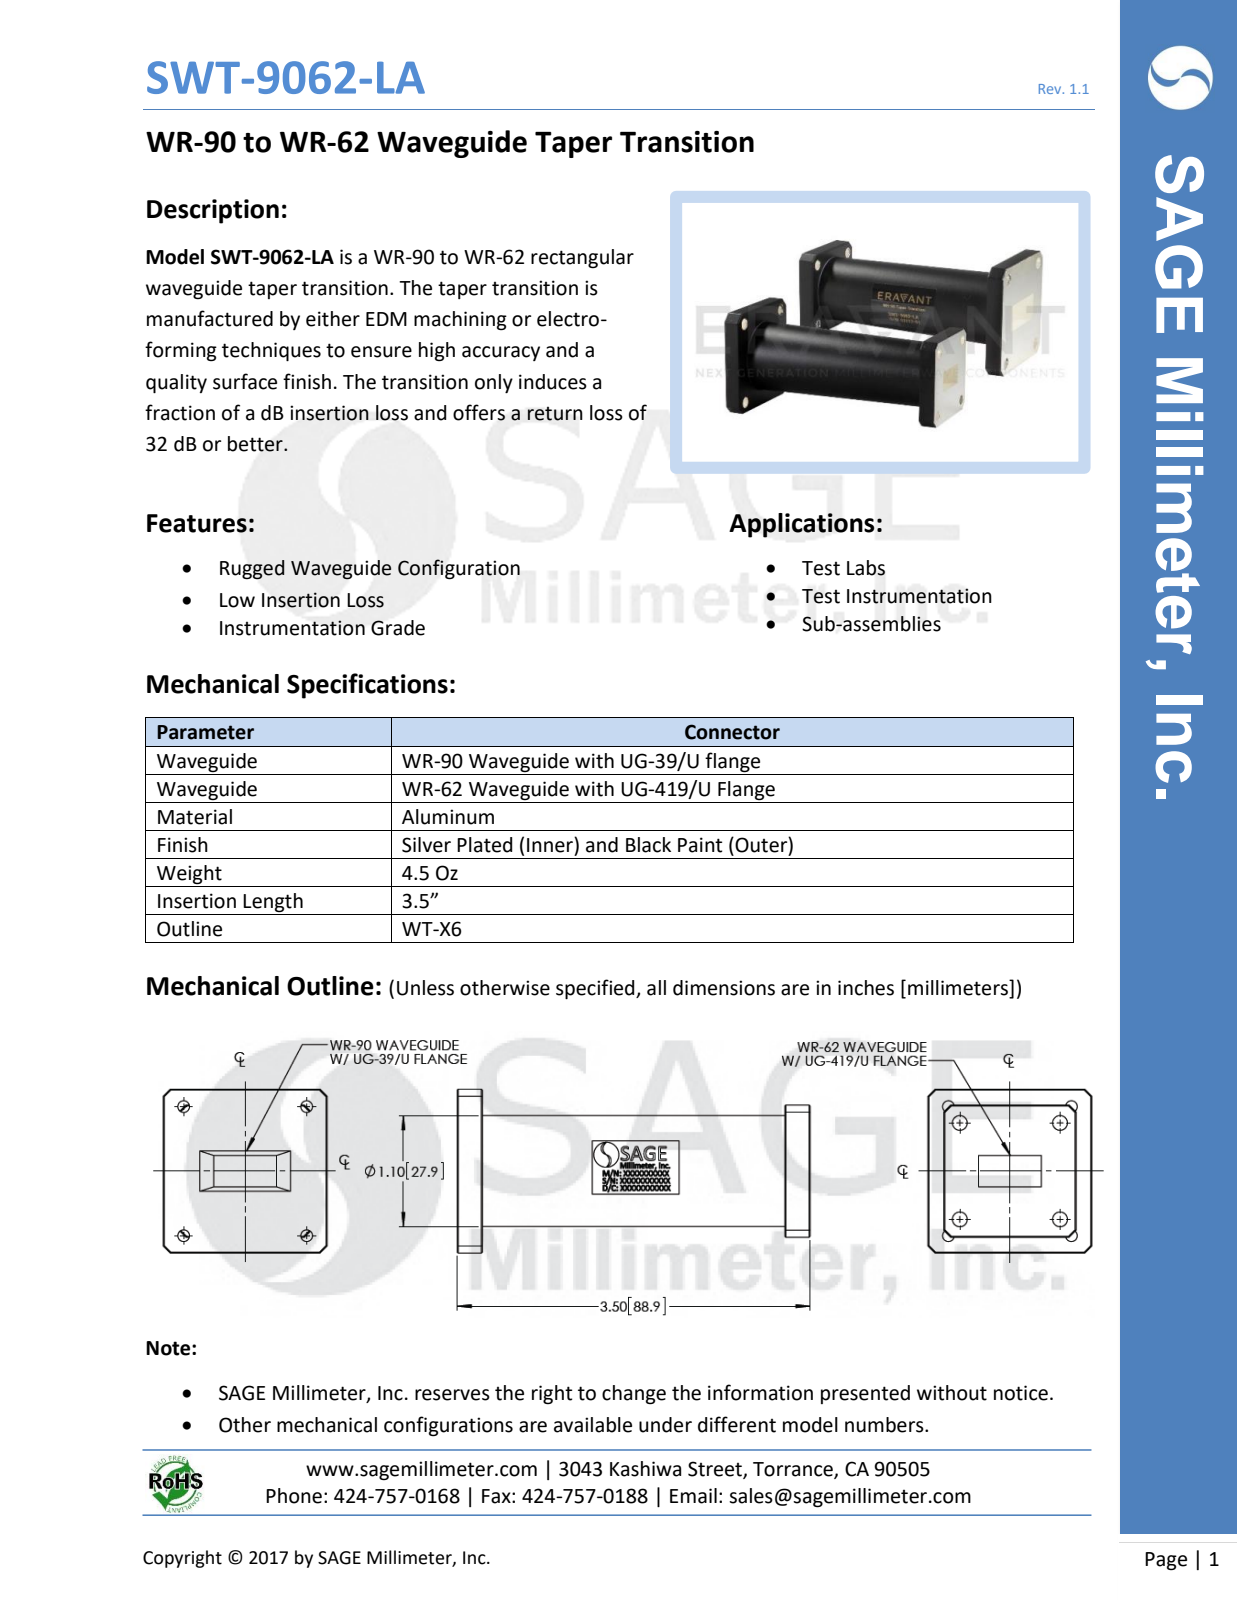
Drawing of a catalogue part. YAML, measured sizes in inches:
part_name: "SWT-9062-LA"
step_written_by: "SolidWorks 2016 (AUTOMOTIVE_DESIGN)"
units: inches
bodies: {solids: 1, faces: 80, planar: 62, cylindrical: 18, other: 0}
overall_size: [3.5, 1.625, 1.625]
volume: 3.895
surface_area: 20.56
round_holes:
  - {diameter: 0.147, count: 4}
  - {diameter: 0.172, count: 4}
round_bosses_or_shafts:
  - {diameter: 1.1, count: 1}
face_to_face_distances: [0.25, 3.25, 3.5, 0.157, 1.469, 1.625, 3, 3.499, 0.249, 3.249]
hole_center_spacings: [0.198, 1.119, 1.124, 1.573, 0.956, 0.994, 1.22, 1.28]
